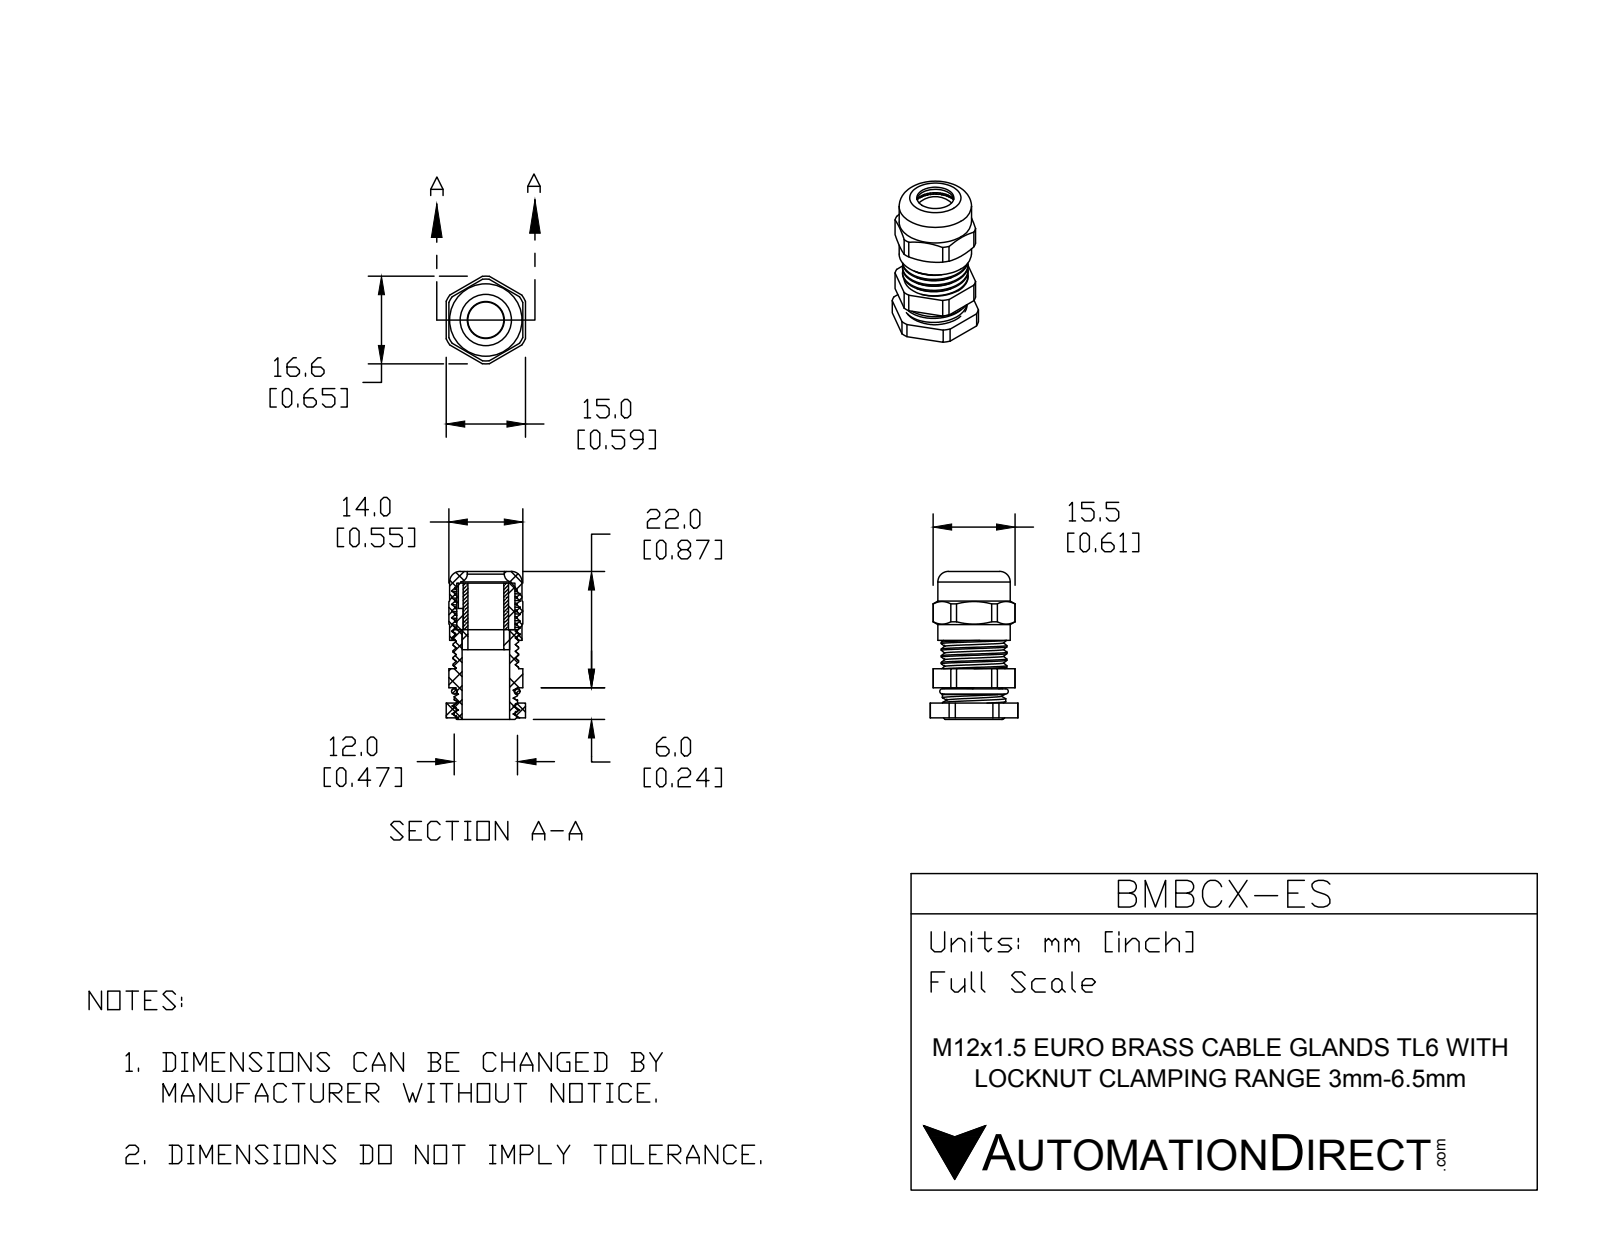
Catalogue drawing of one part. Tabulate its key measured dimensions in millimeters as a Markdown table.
| quantity | value |
| --- | --- |
| part name | BMBCX-ES |
| STEP written by | SolidWorks 2015 (CONFIG_CONTROL_DESIGN) |
| units | millimeters |
| bodies | 6 solids, 254 faces (134 planar, 84 cylindrical, 36 other) |
| overall size | 28 × 16.6 × 15 |
| volume | 2 399 mm³ |
| surface area | 5 051 mm² |
| round holes (diameter × count) | 6.8 × 1, 7 × 1, 8.6 × 1, 9 × 1, 11.19 × 1, 11.79 × 1 |
| round bosses / shafts (diameter × count) | 13.7 × 1, 12.4 × 1, 12 × 1, 11 × 1 |
| partial cylindrical surfaces (radius × count) | 7.75 × 1, 8.3 × 1 |
| main face-to-face distances | 0.5, 14, 14.5, 11, 13.9, 2.8, 16.7, 3.6, 15, 5.7 |
